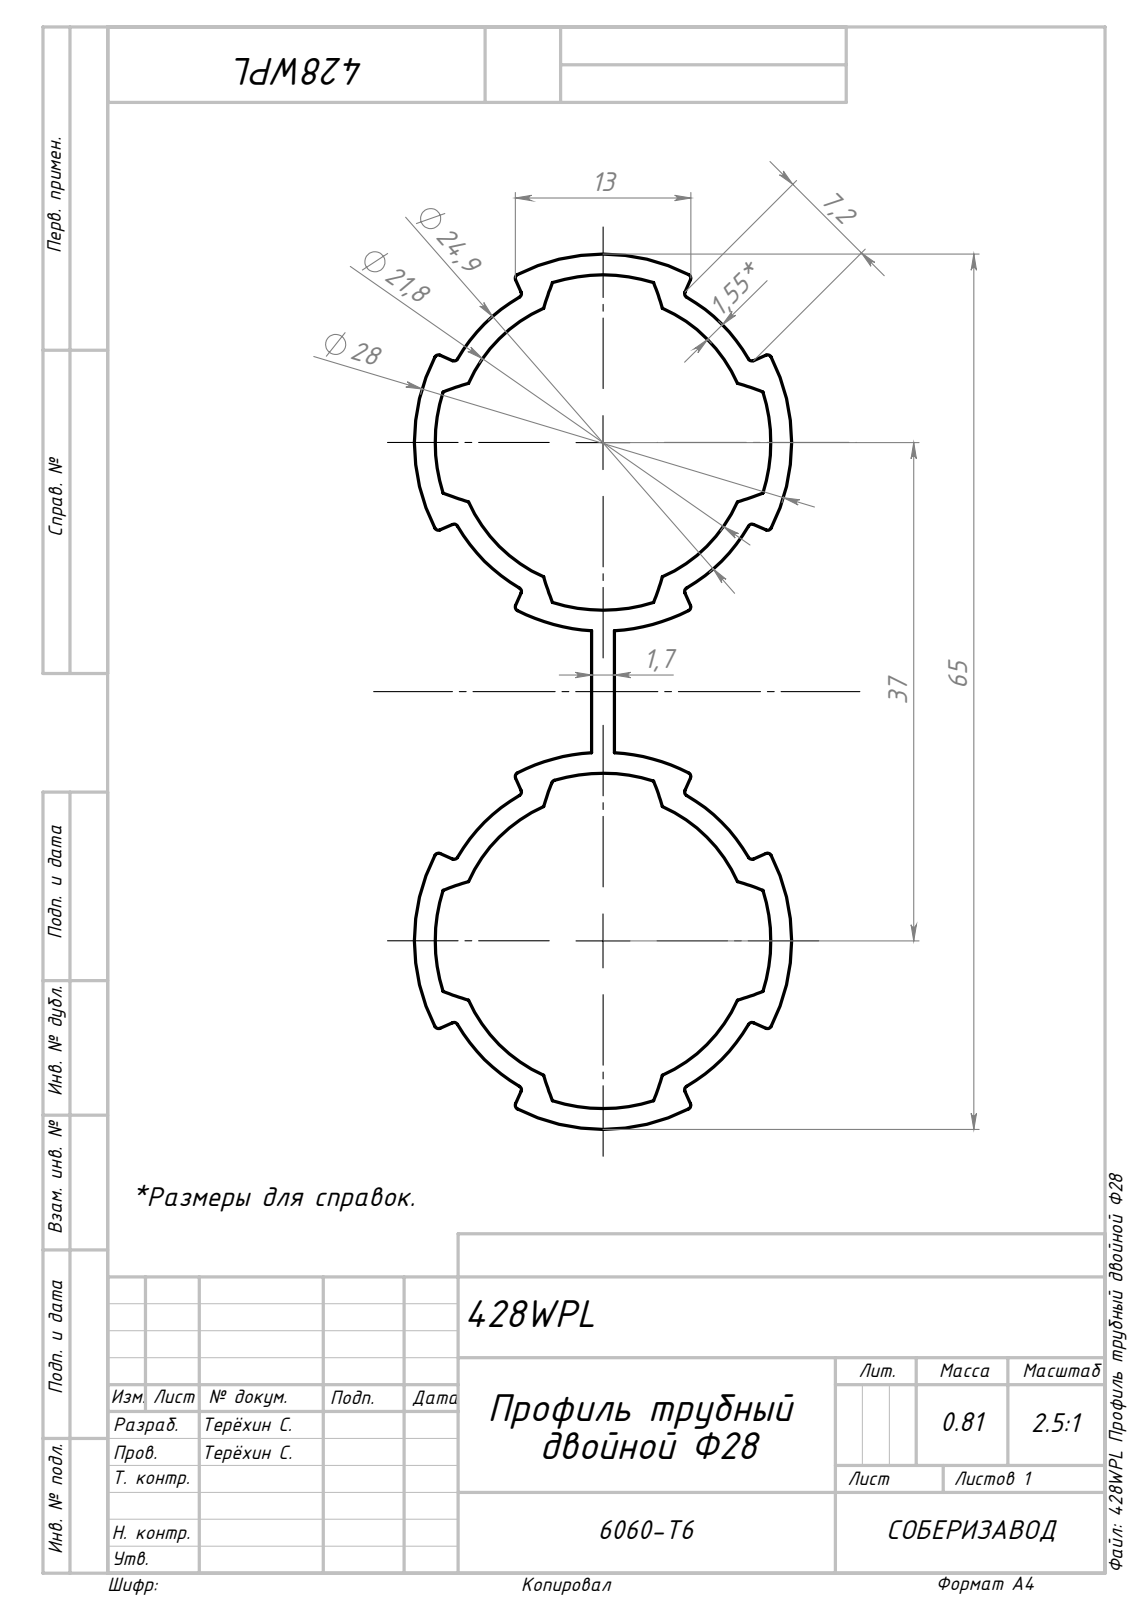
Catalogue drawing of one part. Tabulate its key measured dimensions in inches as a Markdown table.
| quantity | value |
| --- | --- |
| part name | 428WPL Профиль трубный двойной Φ28_00; Сборка1 |
| STEP written by | SolidWorks 2022 (AUTOMOTIVE_DESIGN) |
| units | inches |
| bodies | 1 solid, 115 faces (20 planar, 95 cylindrical, 0 other) |
| overall size | 39.37 × 2.559 × 1.102 |
| volume | 18.66 in³ |
| surface area | 559.5 in² |
| partial cylindrical surfaces (radius × count) | 0.012 × 33, 0.676 × 16, 0.427 × 2, 0.484 × 2, 0.551 × 2 |
| main face-to-face distances | 0.067, 0.047, 0.631, 1.313, 1.36, 0.583, 0.678, 1.265, 39.37 |
